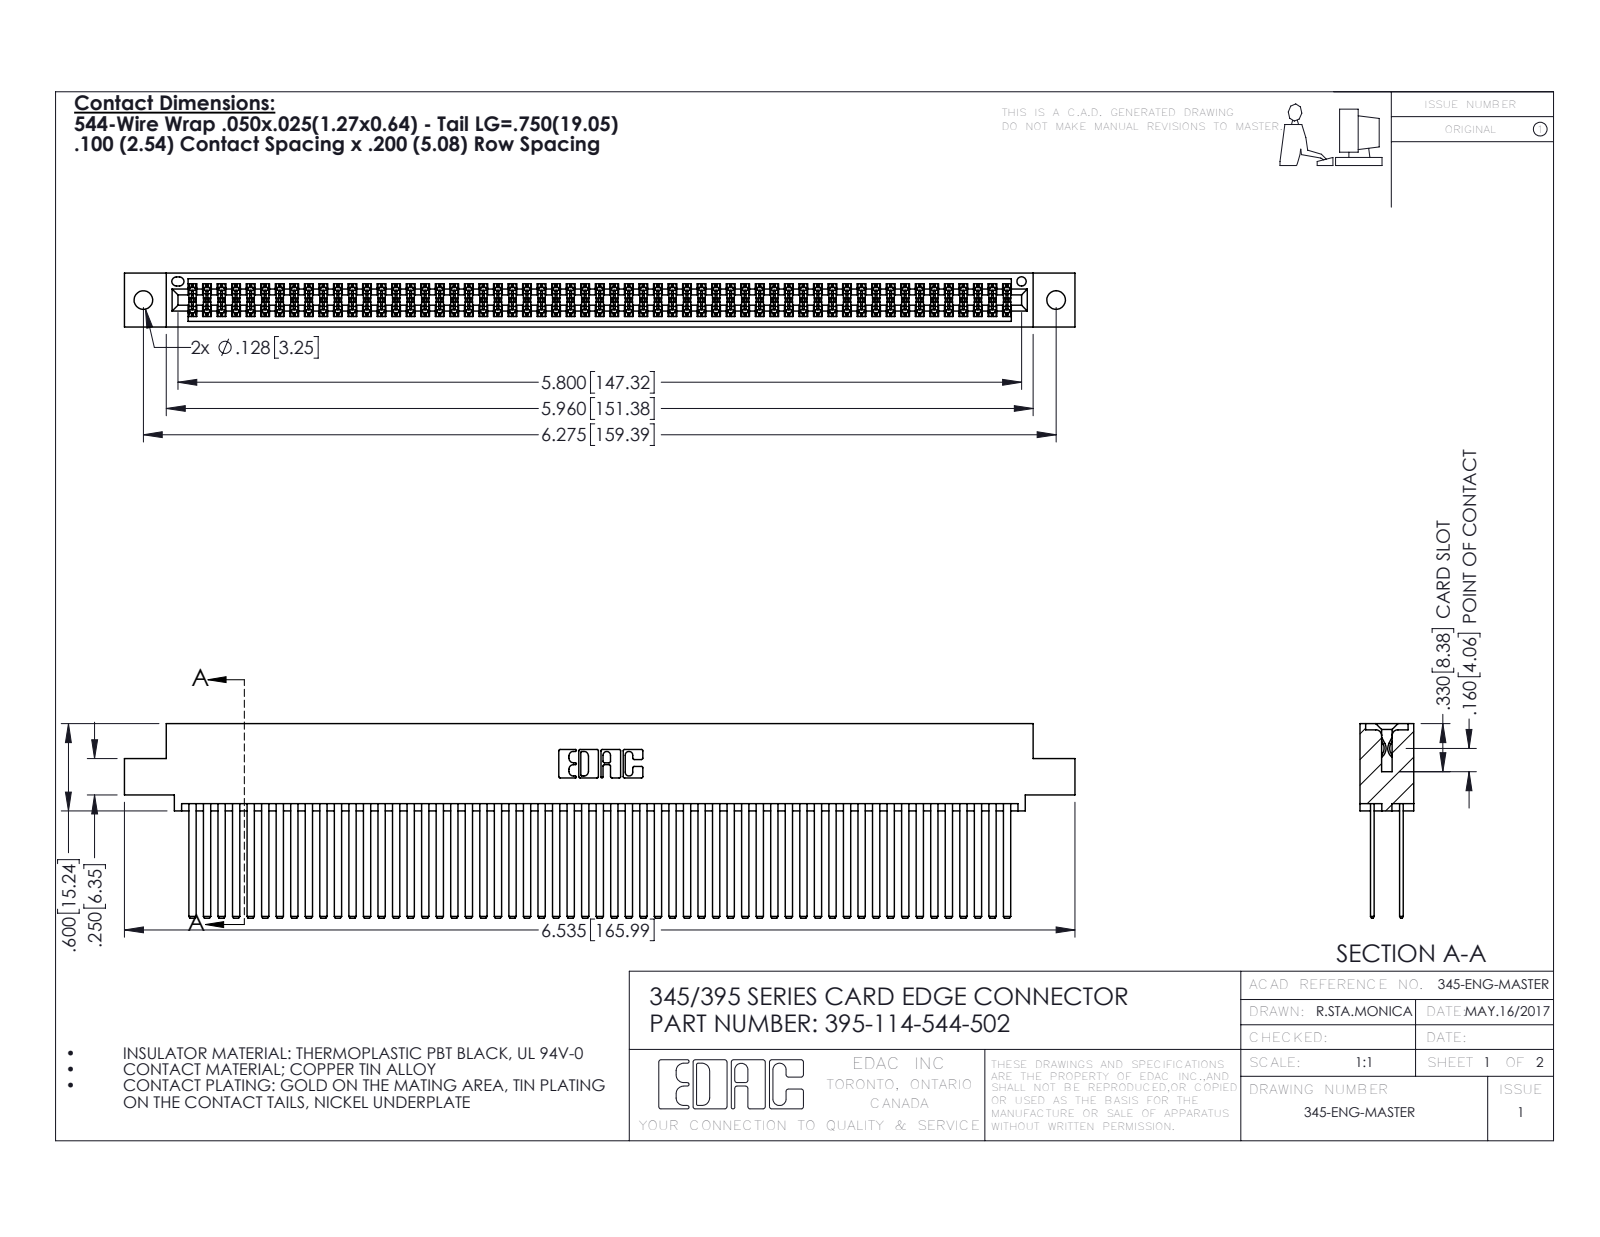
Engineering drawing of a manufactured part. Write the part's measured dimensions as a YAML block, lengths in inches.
part_name: "345 Part_0.110 Offset - 0.128 Dia; 395-114-544-502; 345-292-001_345-293-144"
step_written_by: "SolidWorks 2016 (CONFIG_CONTROL_DESIGN)"
units: inches
bodies: {solids: 115, faces: 5146, planar: 3390, cylindrical: 1756, other: 0}
overall_size: [6.535, 1.337, 0.37]
volume: 1.083
surface_area: 48.1
round_holes:
  - {diameter: 0.128, count: 2}
  - {diameter: 0.064, count: 1}
partial_cylinders:
  - {radius: 0.006, count: 171}
  - {radius: 0.01, count: 22}
  - {radius: 0.007, count: 6}
  - {radius: 0.031, count: 6}
  - {radius: 0.026, count: 3}
  - {radius: 0.014, count: 2}
  - {radius: 0.019, count: 2}
  - {radius: 0.022, count: 2}
face_to_face_distances: [0.2, 0.025, 0.298, 0.072, 0.098, 0.272, 0.225, 0.175, 0.37, 0.05]
hole_center_spacings: [0.27, 6.039, 6.275]
